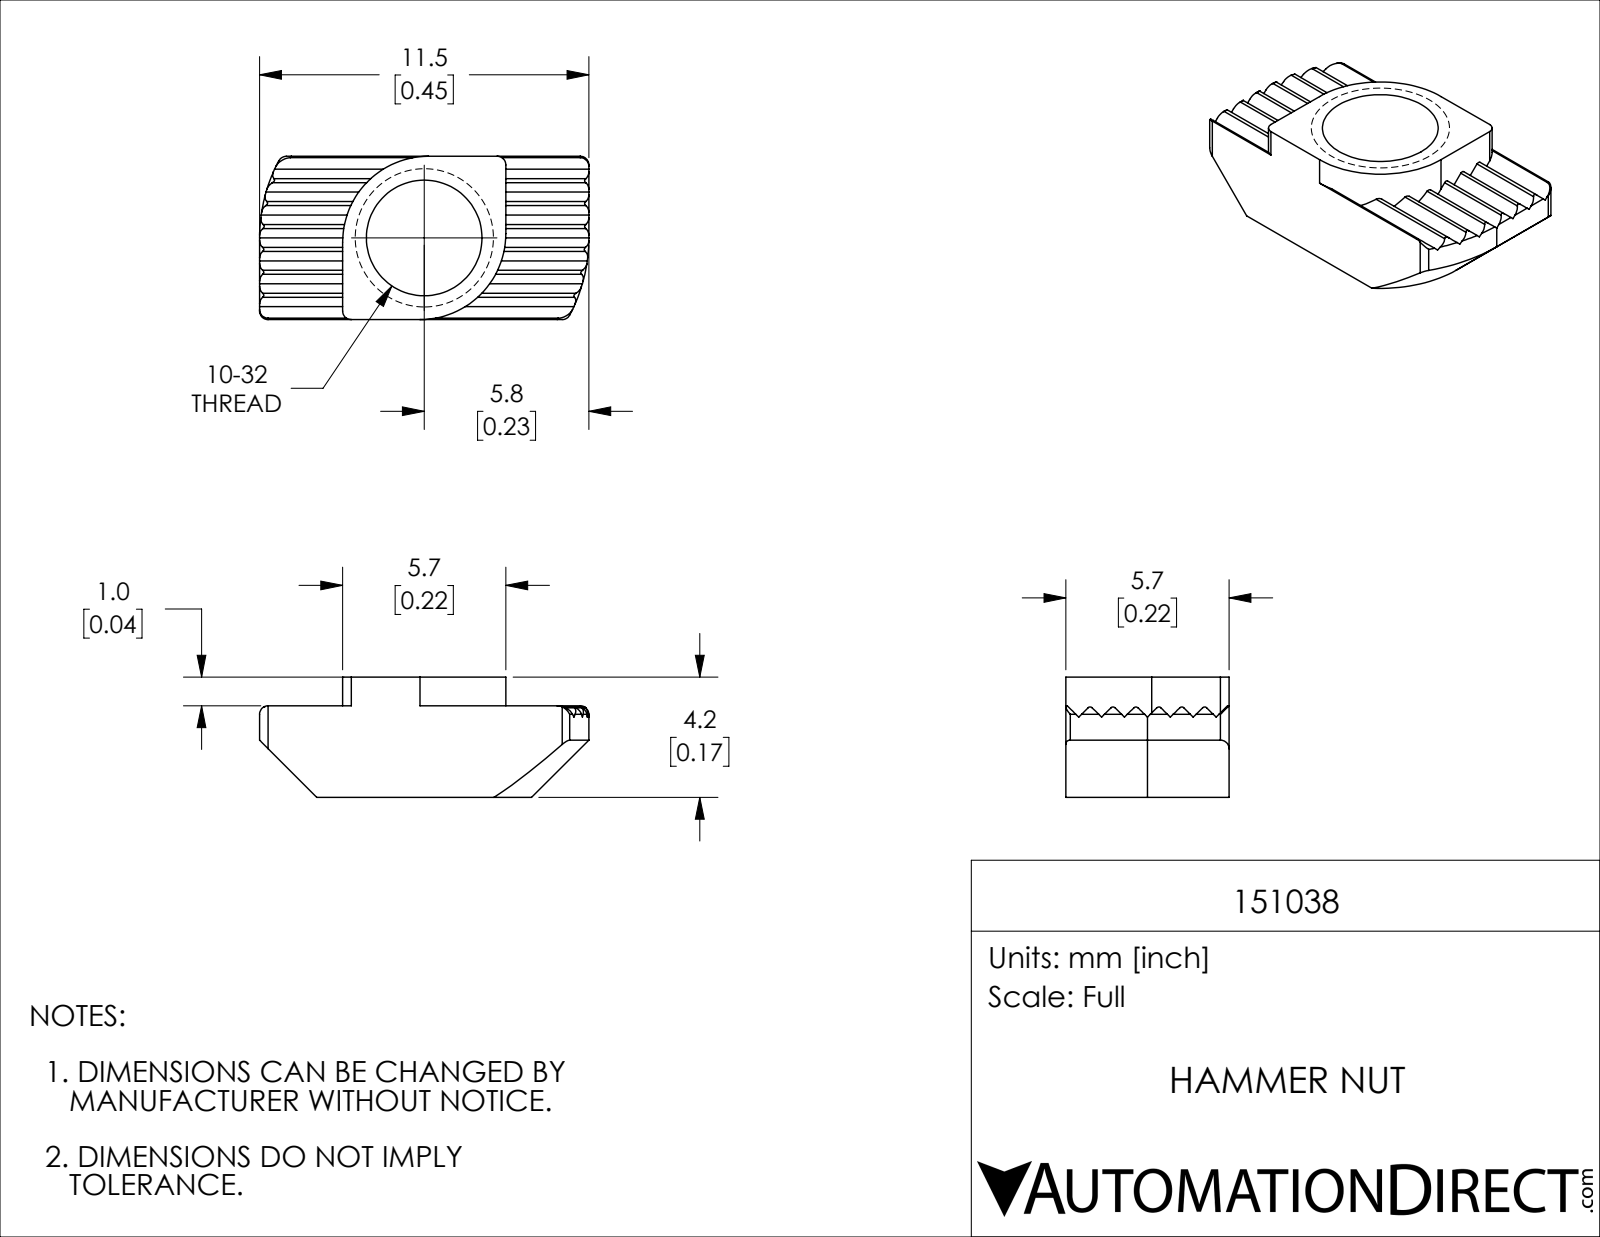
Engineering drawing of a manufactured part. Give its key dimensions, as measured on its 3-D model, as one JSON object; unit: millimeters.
{"part_name": "151038", "step_written_by": "SolidWorks 2021 (CONFIG_CONTROL_DESIGN)", "units": "millimeters", "bodies": {"solids": 1, "faces": 84, "planar": 42, "cylindrical": 32, "other": 10}, "overall_size": [11.5, 5.7, 4.2], "volume_mm3": 149, "surface_area_mm2": 272, "round_holes": [[4.04, 1]], "partial_cylinders_radius": [[0.3, 8], [0.1, 6], [3, 2], [5.75, 1]], "face_to_face_distances": [5.7, 0.57, 1.13, 1.7, 4.2, 2.83, 2.27, 0.56, 3.4, 2.26]}
